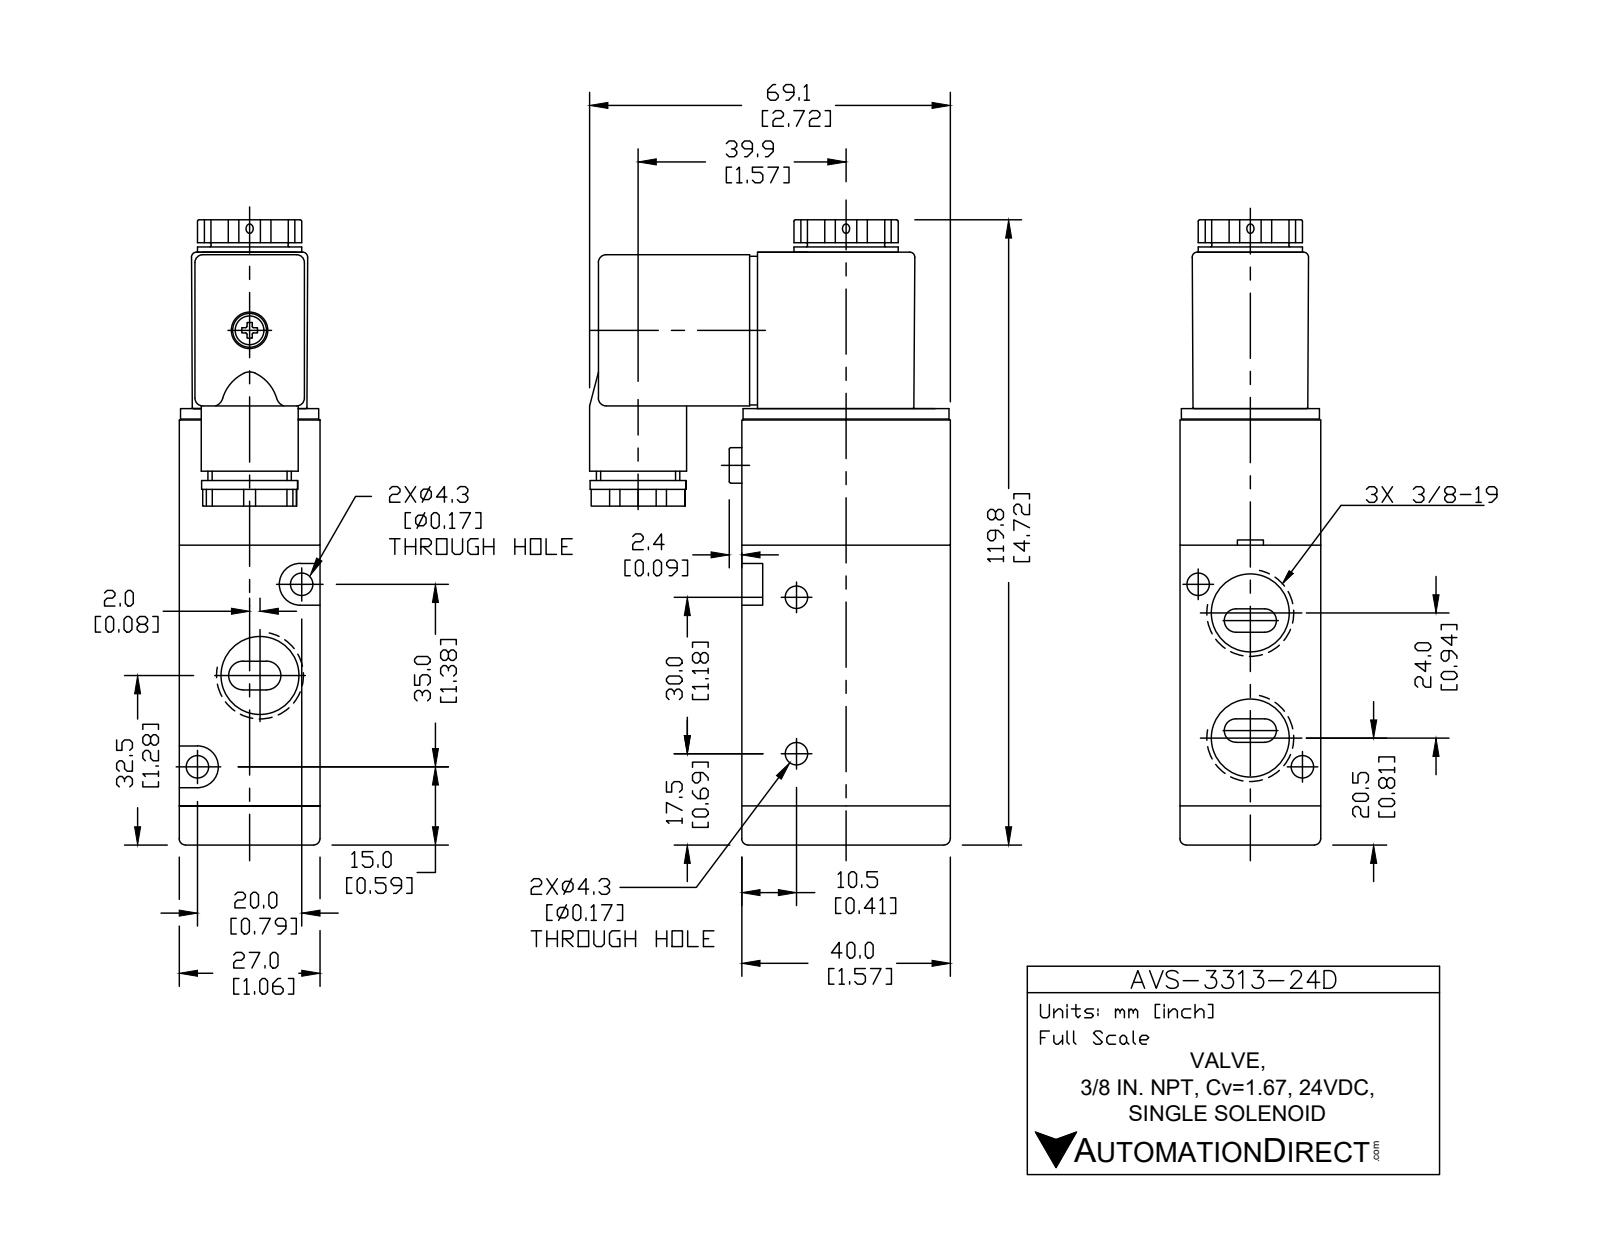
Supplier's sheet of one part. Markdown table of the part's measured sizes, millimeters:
| quantity | value |
| --- | --- |
| part name | AVS-3313-24D |
| STEP written by | SolidWorks 2015 (CONFIG_CONTROL_DESIGN) |
| units | millimeters |
| bodies | 4 solids, 156 faces (81 planar, 53 cylindrical, 22 other) |
| overall size | 119.9 × 69.1 × 27 |
| volume | 124 534 mm³ |
| surface area | 29 364 mm² |
| round holes (diameter × count) | 4.3 × 4, 14.27 × 3, 9.3 × 1 |
| round bosses / shafts (diameter × count) | 20 × 1, 18.6 × 1, 18.4 × 1, 16 × 1, 14.8 × 1, 6.8 × 1 |
| partial cylindrical surfaces (radius × count) | 0.5 × 11, 1 × 10, 4 × 2 |
| main face-to-face distances | 50, 27, 3, 24, 7.5, 57.5, 21, 2.26, 2.27, 40 |
| hole center spacings | 11.41, 12.17, 31.15, 19.24, 21.22, 24, 30, 40.31 |
